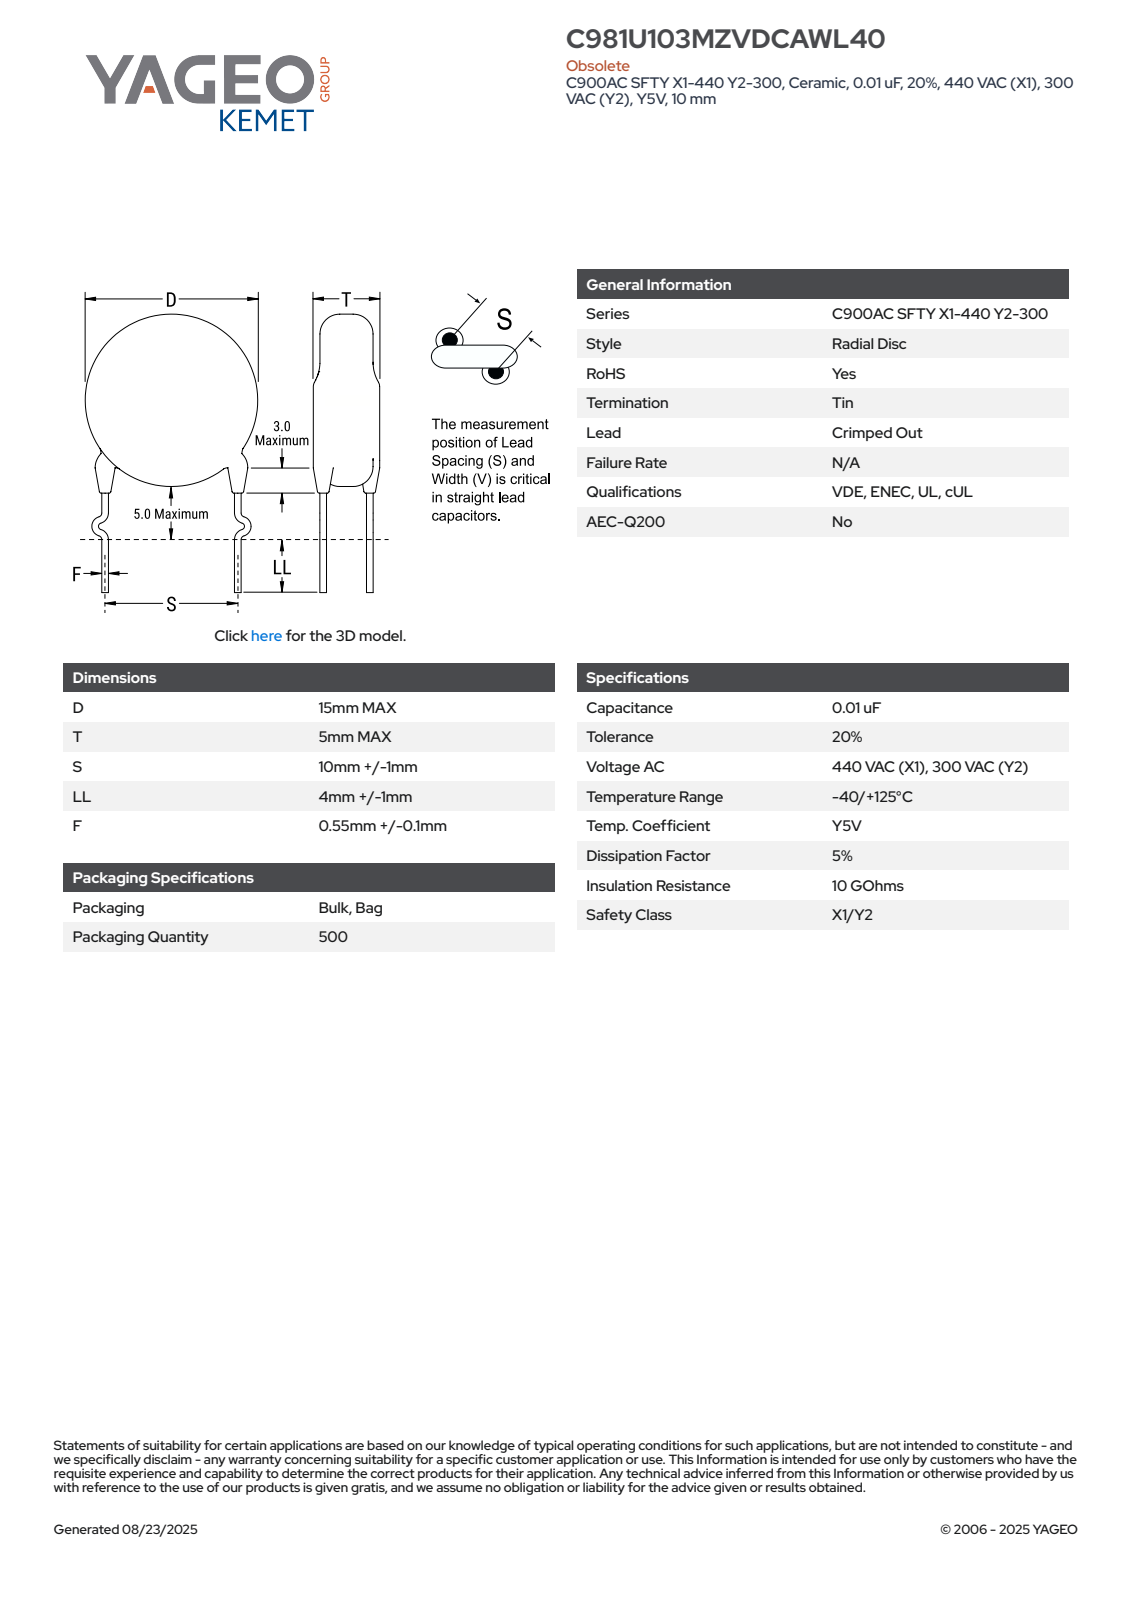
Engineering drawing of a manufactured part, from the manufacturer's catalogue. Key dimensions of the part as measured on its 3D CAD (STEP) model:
Part name (STEP PRODUCT): CCD_KCOC900_D15T5S10LL5F0.55
STEP written by: SolidWorks 2014 (AUTOMOTIVE_DESIGN)
Units: millimetres
Bodies: 4 solids, 85 faces (63 planar, 6 cylindrical, 16 other)
Overall size (bounding box): 25 × 15.21 × 5
Volume: 876 mm³ · Surface area: 627 mm²
Round bosses / shafts (diameter × count): ⌀1.2 ×2, ⌀15 ×1
Main face-to-face distances: 5, 8.29, 6.74, 1.55, 0.42, 0.68, 6.37, 1.26, 0.97, 0.58
